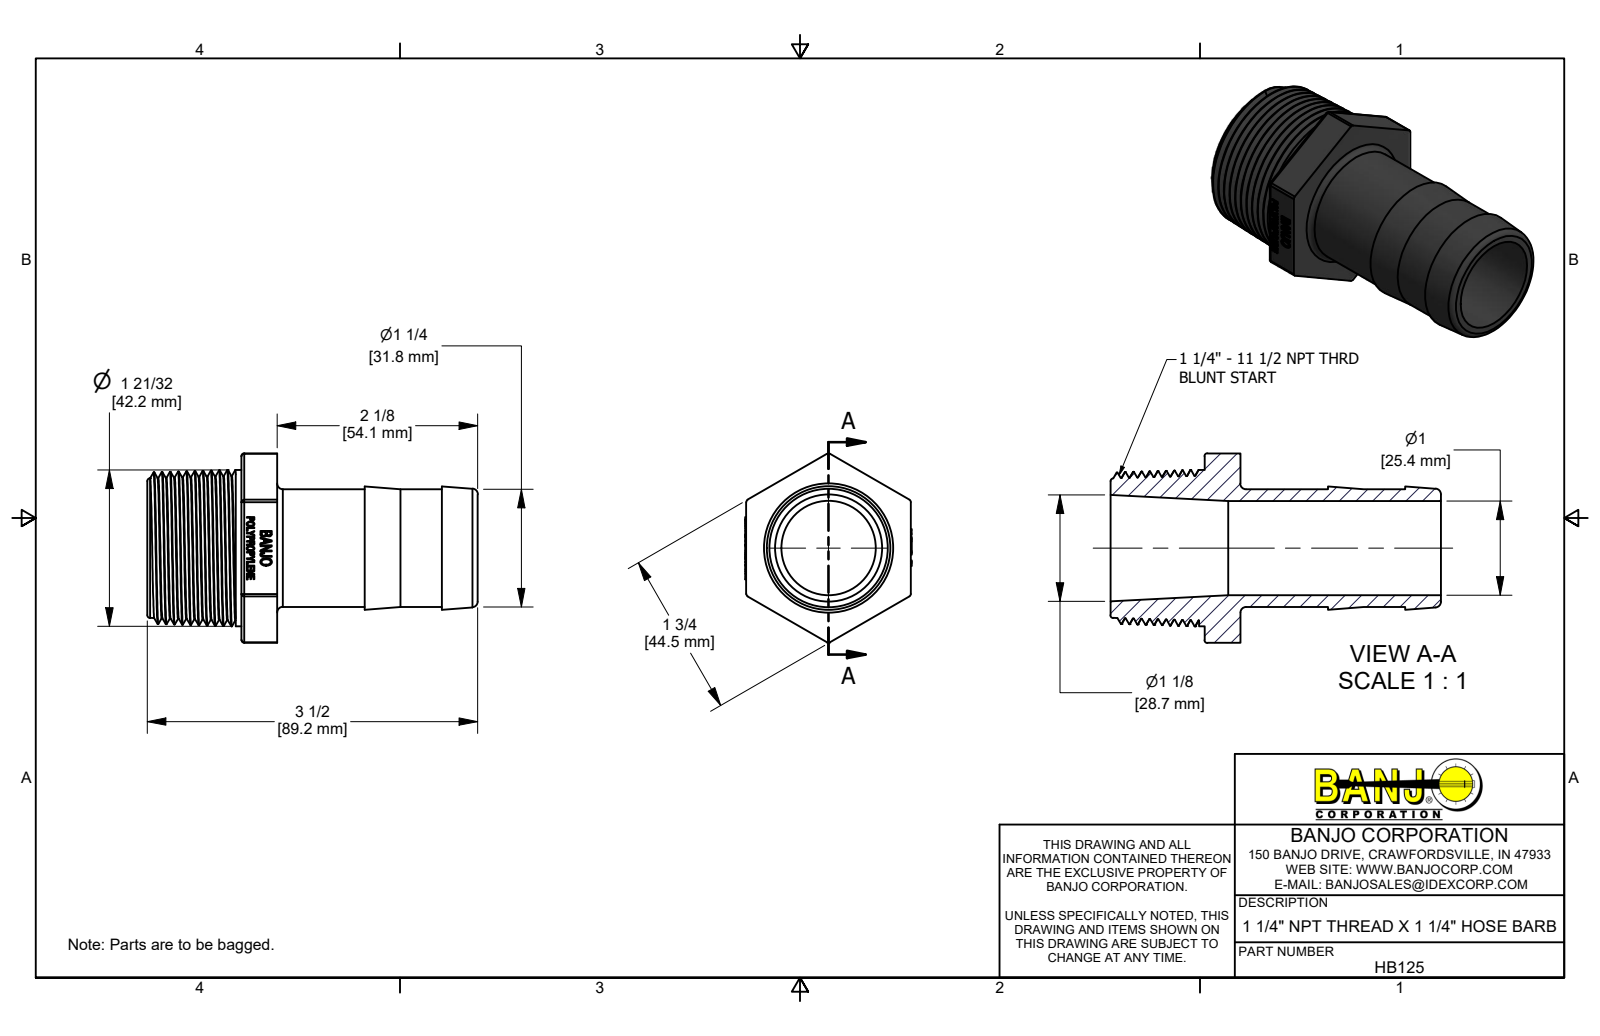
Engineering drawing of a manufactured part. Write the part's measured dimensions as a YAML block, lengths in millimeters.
part_name: "HB125"
step_written_by: "Autodesk Inventor 2014 (AUTOMOTIVE_DESIGN)"
units: millimeters
bodies: {solids: 1, faces: 413, planar: 266, cylindrical: 24, other: 123}
overall_size: [89.15, 51.09, 44.96]
volume: 44549
surface_area: 21802
round_holes:
  - {diameter: 25.4, count: 1}
round_bosses_or_shafts:
  - {diameter: 42.16, count: 1}
  - {diameter: 31.75, count: 1}
partial_cylinders:
  - {radius: 0.76, count: 12}
  - {radius: 11.02, count: 1}
  - {radius: 16.13, count: 1}
face_to_face_distances: [44.44, 35.05, 9.65, 54.1, 25.4, 89.15, 63.75, 23.88, 1.52, 11.17]
